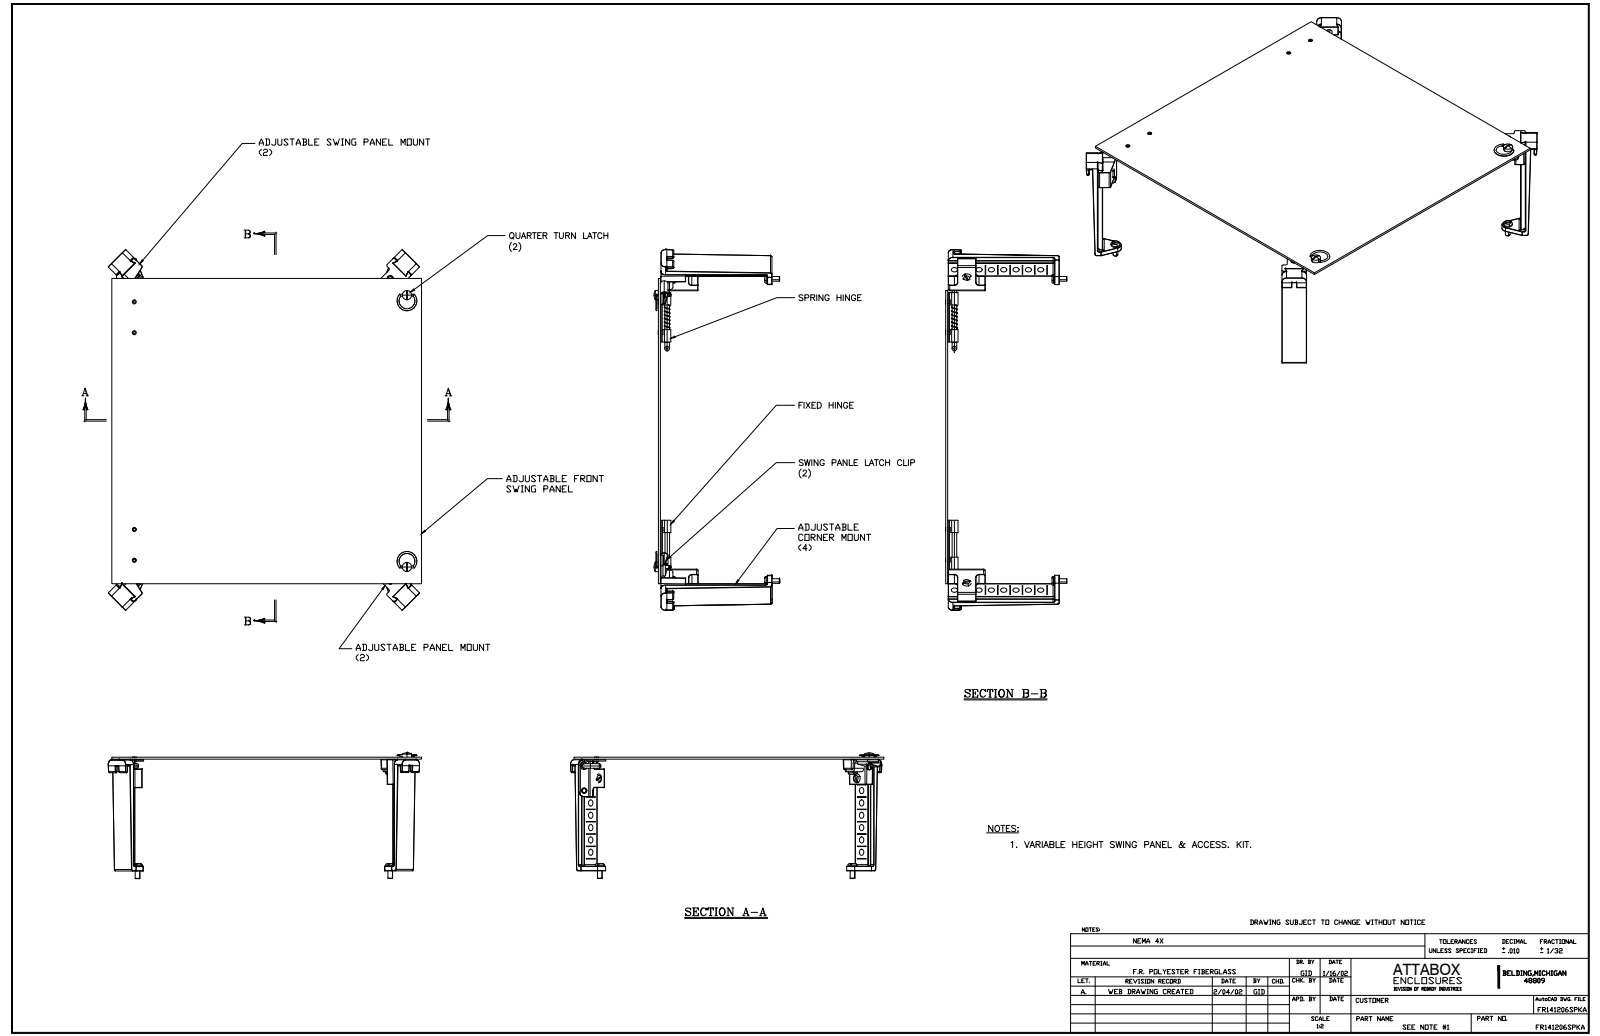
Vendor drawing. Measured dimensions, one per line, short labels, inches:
name: FR141206SPKA
written by: SolidWorks 2019 (AUTOMOTIVE_DESIGN)
unit: in
bodies: 48 solids, 1801 faces (826 planar, 481 cylindrical, 494 other)
size: 14.622 × 12.624 × 4.703
volume: 21.36 in³; area: 446.7 in²
holes: 36× ⌀0.25, 6× ⌀0.156, 6× ⌀0.253, 4× ⌀0.05, 4× ⌀0.14, 4× ⌀0.144, 4× ⌀0.217, 4× ⌀0.22, 2× ⌀0.197, 2× ⌀0.312, 2× ⌀0.35, 1× ⌀0.153
bosses: 10× ⌀0.19, 6× ⌀0.373, 6× ⌀0.246, 4× ⌀0.433, 4× ⌀0.315, 4× ⌀0.16, 4× ⌀0.079, 2× ⌀0.394
rounds: 216× R0.01, 44× R0.06, 10× R0.062, 8× R0.025, 8× R0.063, 6× R0.13, 4× R0.049, 4× R0.19
face distances: 0.08, 16.953, 0.203, 17.156, 1, 1.413, 7.473, 9.886, 7.27, 9.683
hole spacings: 0.5, 1.498, 1, 1.731, 1.5, 2.06, 1.413, 2
